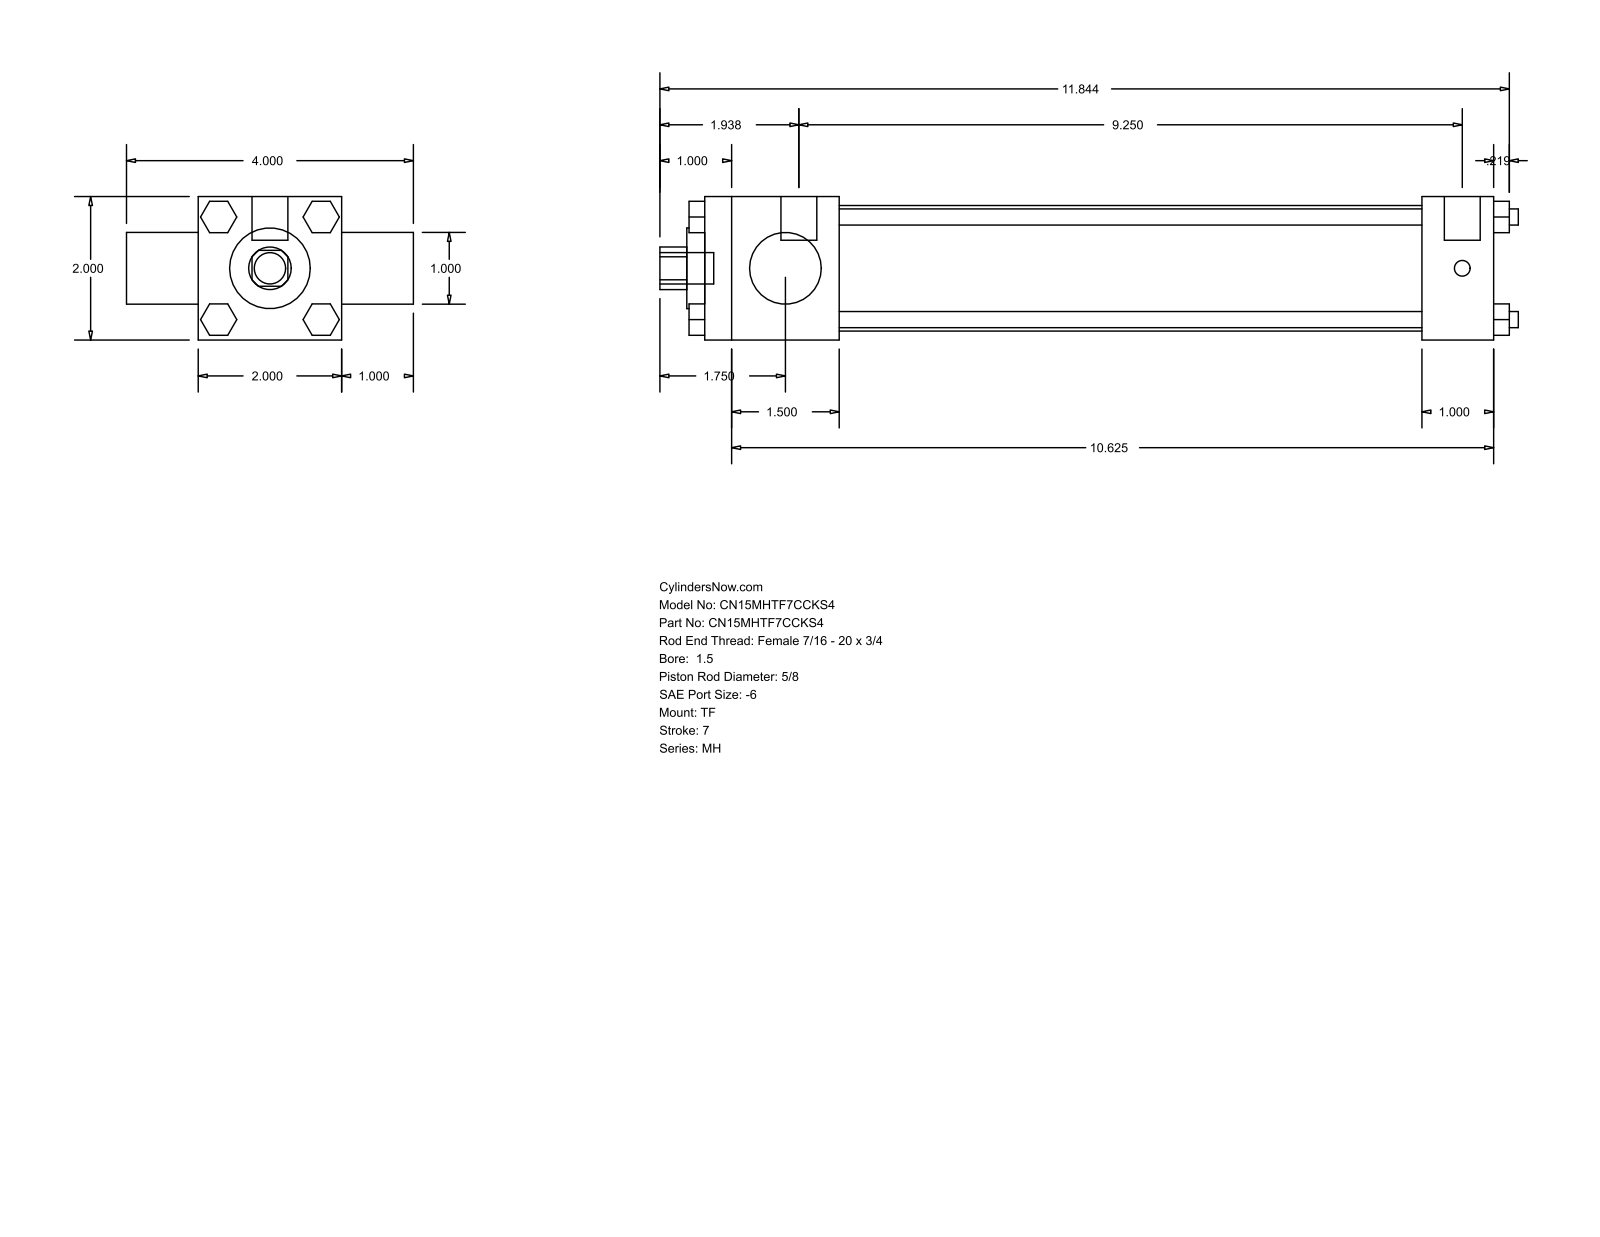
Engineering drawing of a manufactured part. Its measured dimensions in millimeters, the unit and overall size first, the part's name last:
Units: millimetres
Overall size (bounding box): 304.01 × 101.6 × 50.8
Round holes (diameter × count): ⌀15.88 ×1, ⌀25.4 ×1, ⌀28.57 ×1, ⌀44.45 ×1
Round bosses / shafts (diameter × count): ⌀5.71 ×4, ⌀5.56 ×3, ⌀12.7 ×2, ⌀11.11 ×1
Partial cylindrical surfaces — rounded edges, fillets, slot ends (radius × count): R7.54 ×1
Main face-to-face distances: 50.8, 279.39, 25.4, 76.2, 47.62, 231.77, 254, 206.38, 25.39, 5.56
Bodies: 0 solids, 120 faces (92 planar, 28 cylindrical, 0 other)
Part name (STEP PRODUCT): MH_TF__0150_0.625
STEP written by: GSSL Pune (CONFIG_CONTROL_DESIGN)
